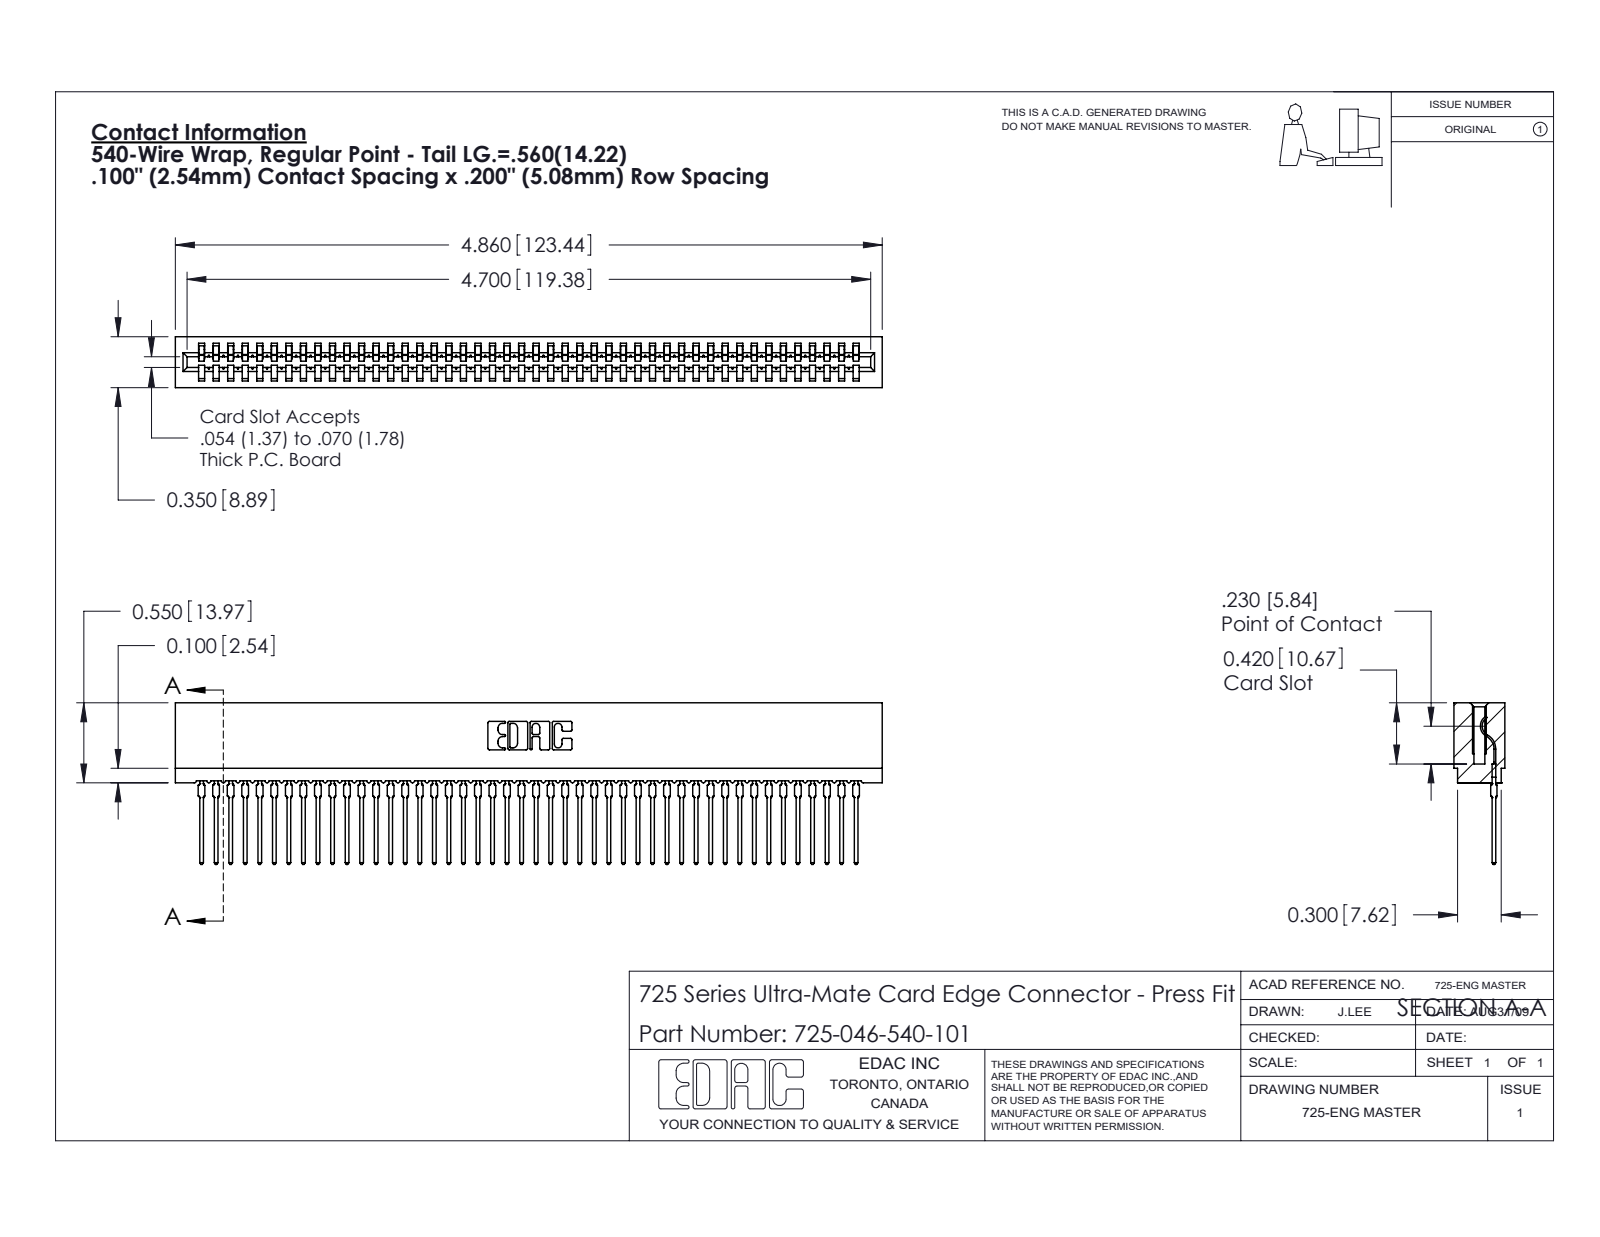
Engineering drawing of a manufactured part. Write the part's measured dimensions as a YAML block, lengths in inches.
part_name: "725-046-540-101; 745-292-001_540; 725 Part_Insulator Option - 01"
step_written_by: "SolidWorks 2020 (CONFIG_CONTROL_DESIGN)"
units: inches
bodies: {solids: 47, faces: 5247, planar: 3137, cylindrical: 914, other: 1196}
overall_size: [4.86, 1.111, 0.35]
volume: 0.577
surface_area: 29.09
partial_cylinders:
  - {radius: 0.015, count: 92}
  - {radius: 0.021, count: 92}
  - {radius: 0.01, count: 22}
  - {radius: 0.007, count: 6}
  - {radius: 0.031, count: 6}
  - {radius: 0.005, count: 4}
  - {radius: 0.011, count: 4}
  - {radius: 0.026, count: 3}
face_to_face_distances: [0.35, 0.2, 0.212, 0.138, 0.063, 0.287, 0.1, 0.045, 0.305, 0.093]
